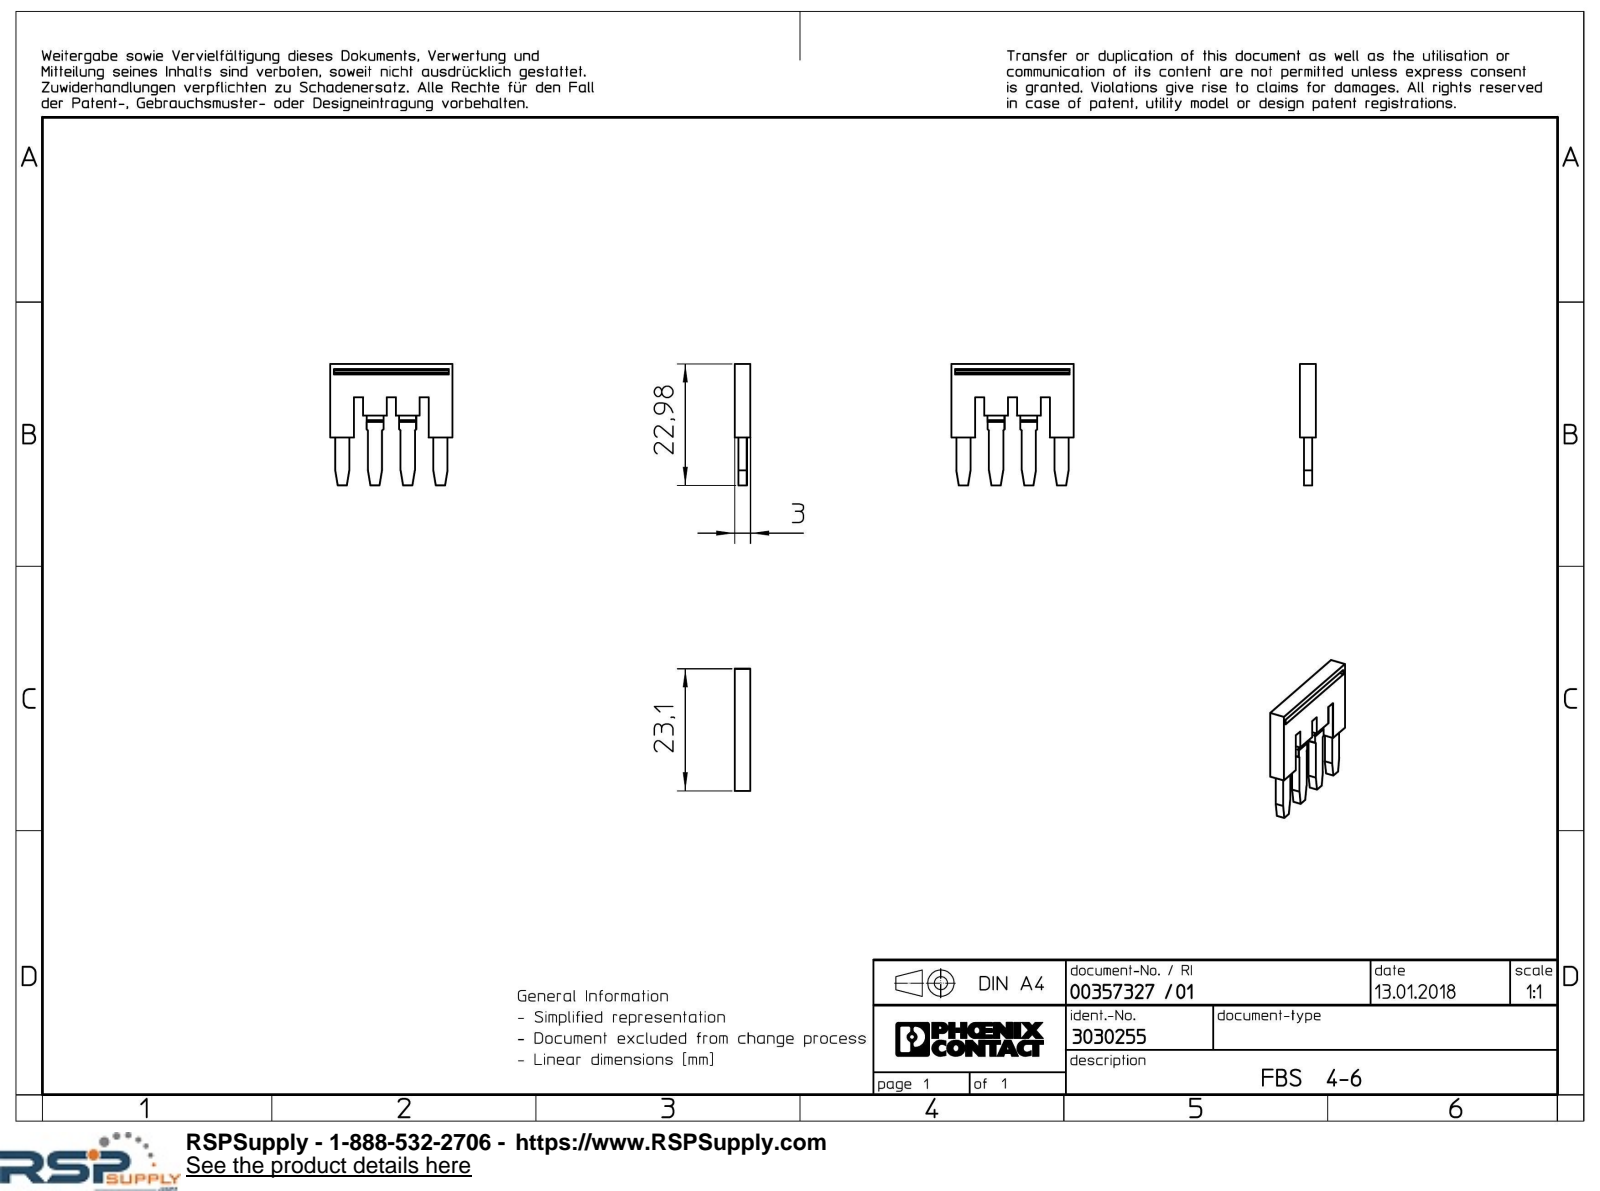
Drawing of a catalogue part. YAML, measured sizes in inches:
part_name: "FBS_4-6_select"
step_written_by: "Creo Elements/Direct Modeling 20.1A 29-Sep-2018 (C) Parametric Technology GmbH (AUTOMOTIVE_DESIGN)"
units: inches
bodies: {solids: 1, faces: 76, planar: 76, cylindrical: 0, other: 0}
overall_size: [0.909, 0.905, 0.118]
volume: 0.054
surface_area: 1.92
face_to_face_distances: [0.028, 0.091, 0.118, 0.244, 0.063, 0.141, 0.036, 0.488, 0.177, 0.732]
